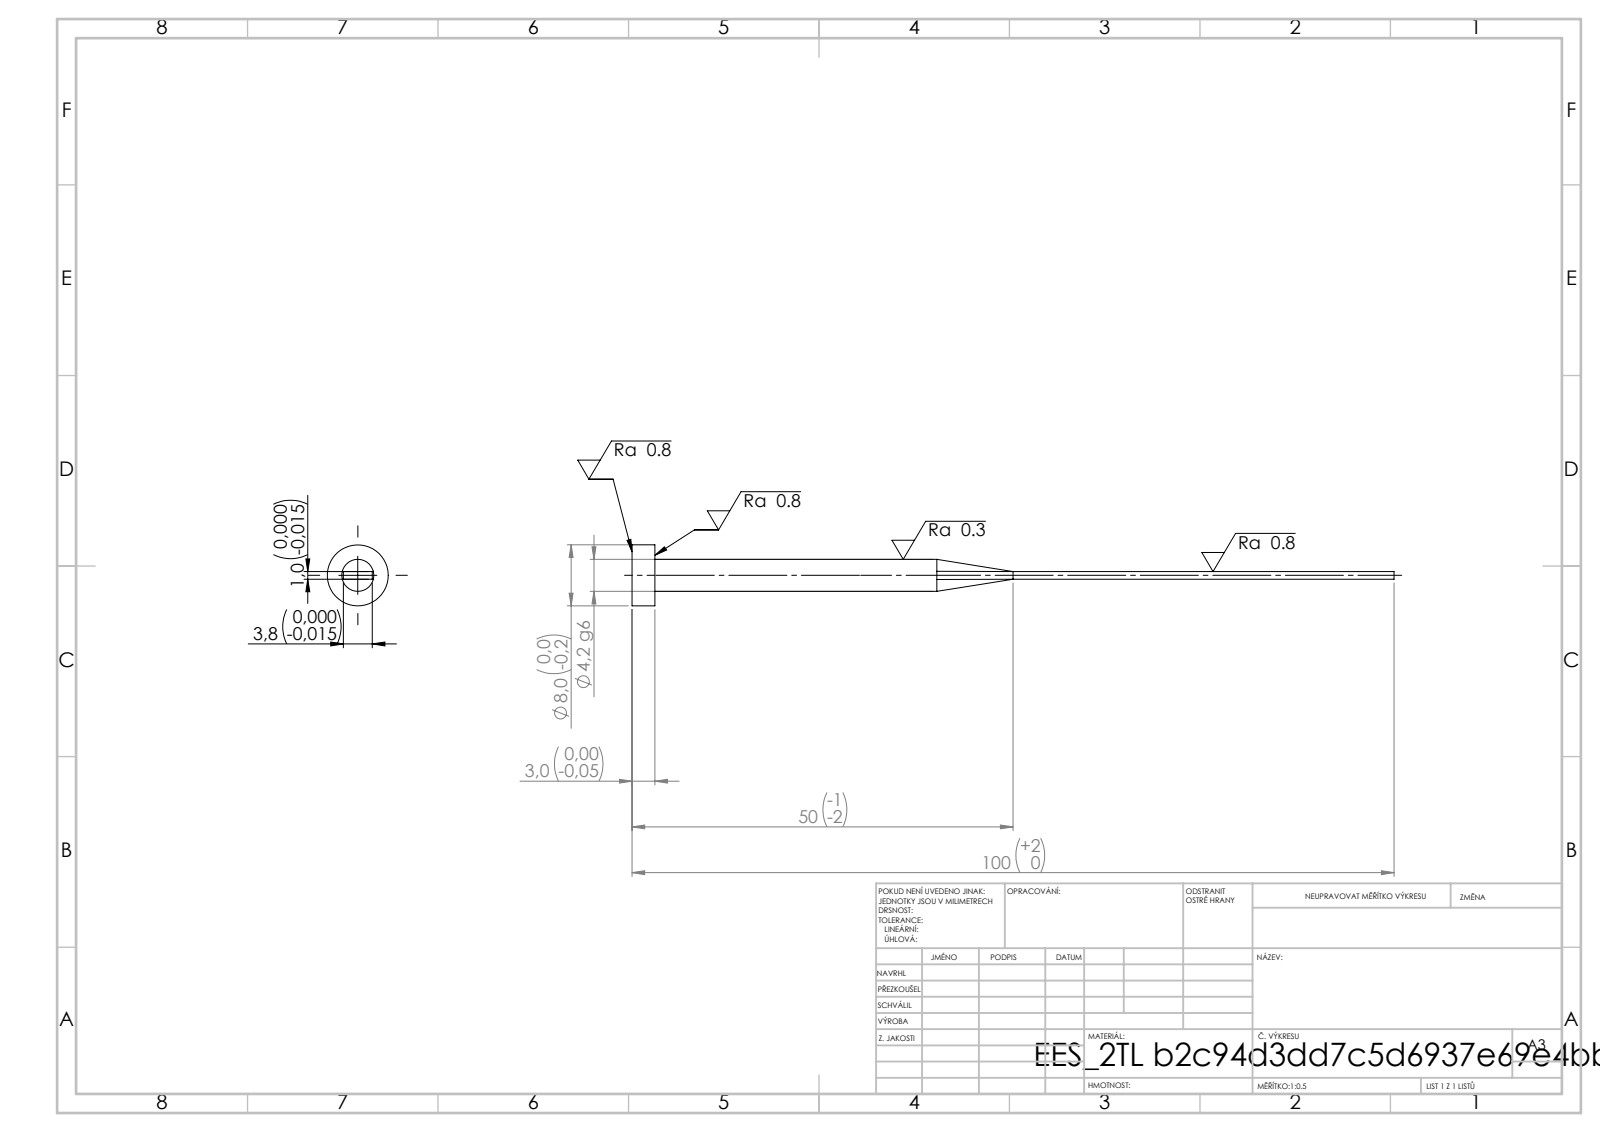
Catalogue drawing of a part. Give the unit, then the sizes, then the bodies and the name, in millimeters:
Units: millimetres
Overall size (bounding box): 100 × 8 × 8
Round bosses / shafts (diameter × count): ⌀8 ×1, ⌀4.2 ×1
Main face-to-face distances: 1, 3.8, 3, 100, 97
Volume: 938 mm³ · Surface area: 1 244 mm²
Bodies: 1 solid, 15 faces (7 planar, 4 cylindrical, 4 other)
STEP written by: SolidWorks 2019 (CONFIG_CONTROL_DESIGN)
